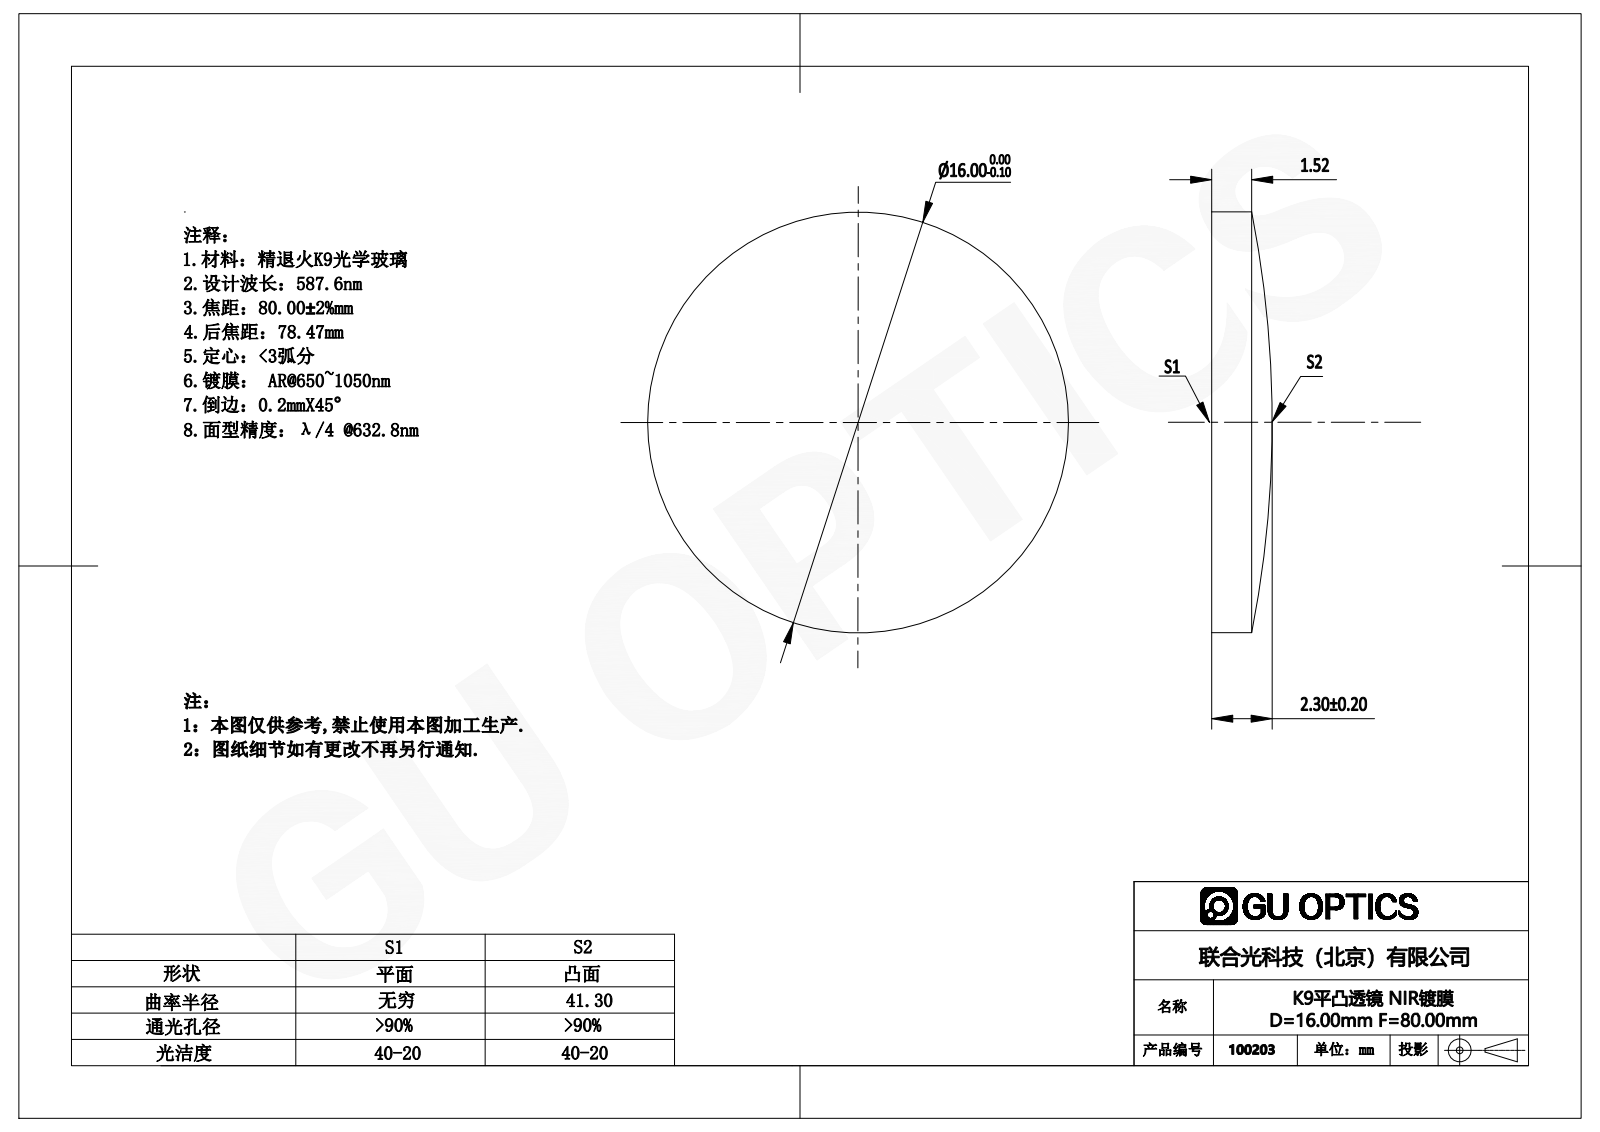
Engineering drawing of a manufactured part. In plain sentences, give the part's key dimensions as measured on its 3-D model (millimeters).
The part is named "100203". Its 3-D file was written by "SolidWorks 2016 (AUTOMOTIVE_DESIGN)". It is 1 solid with 5 faces: 1 planar, 2 cylindrical and 2 other. Overall it measures 16 by 16 by 2.3 millimeters. Its volume is 384 cubic millimeters and its surface area 480 square millimeters. Round bosses or shafts: 1 of diameter 16.
